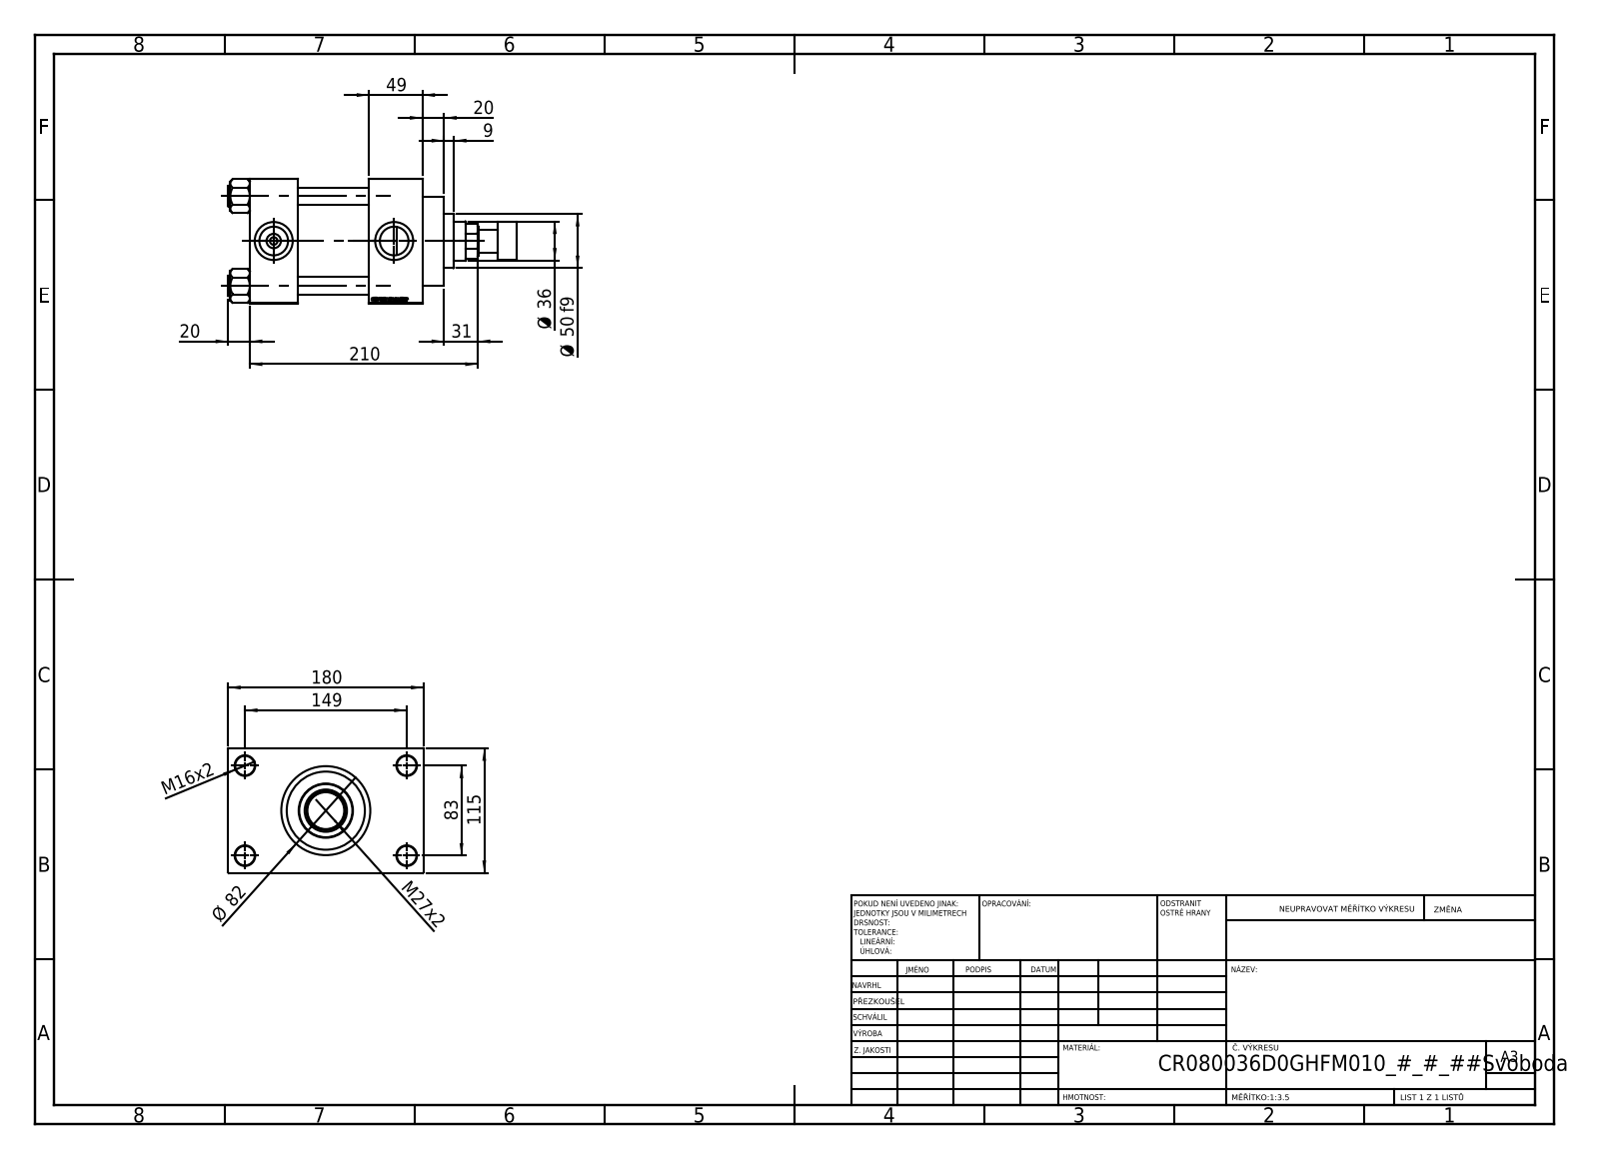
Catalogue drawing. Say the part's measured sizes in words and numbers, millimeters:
The part is named "V215CR_D_Body; V215CR_VCP_D; V215CR_ROD_END_F; V215CR_D_TYCINKA (+2 more)". Its 3-D file was written by "SolidWorks 2019 (CONFIG_CONTROL_DESIGN)". It is 12 solids with 1165 faces: 549 planar, 92 cylindrical and 524 other. Overall it measures 266 by 180 by 115 millimeters. Its volume is 2 003 000 cubic millimeters and its surface area 302 161 square millimeters. Round holes: 4 of diameter 16, 4 of diameter 18, 2 of diameter 7, 2 of diameter 26.44, 2 of diameter 35, 1 of diameter 25.5, 1 of diameter 36, 1 of diameter 39, 1 of diameter 61, 1 of diameter 72, 1 of diameter 80. Round bosses or shafts: 4 of diameter 19, 1 of diameter 86, 1 of diameter 82, 1 of diameter 50, 1 of diameter 35, 1 of diameter 21. The main face-to-face distances are 115, 66, 49, 110, 44, 159, 32.5, 147.5, 20, 69. The hole center spacings are 33.15, 58.48, 82.7, 85.28, 89.24, 115.85, 142.43, 83.
